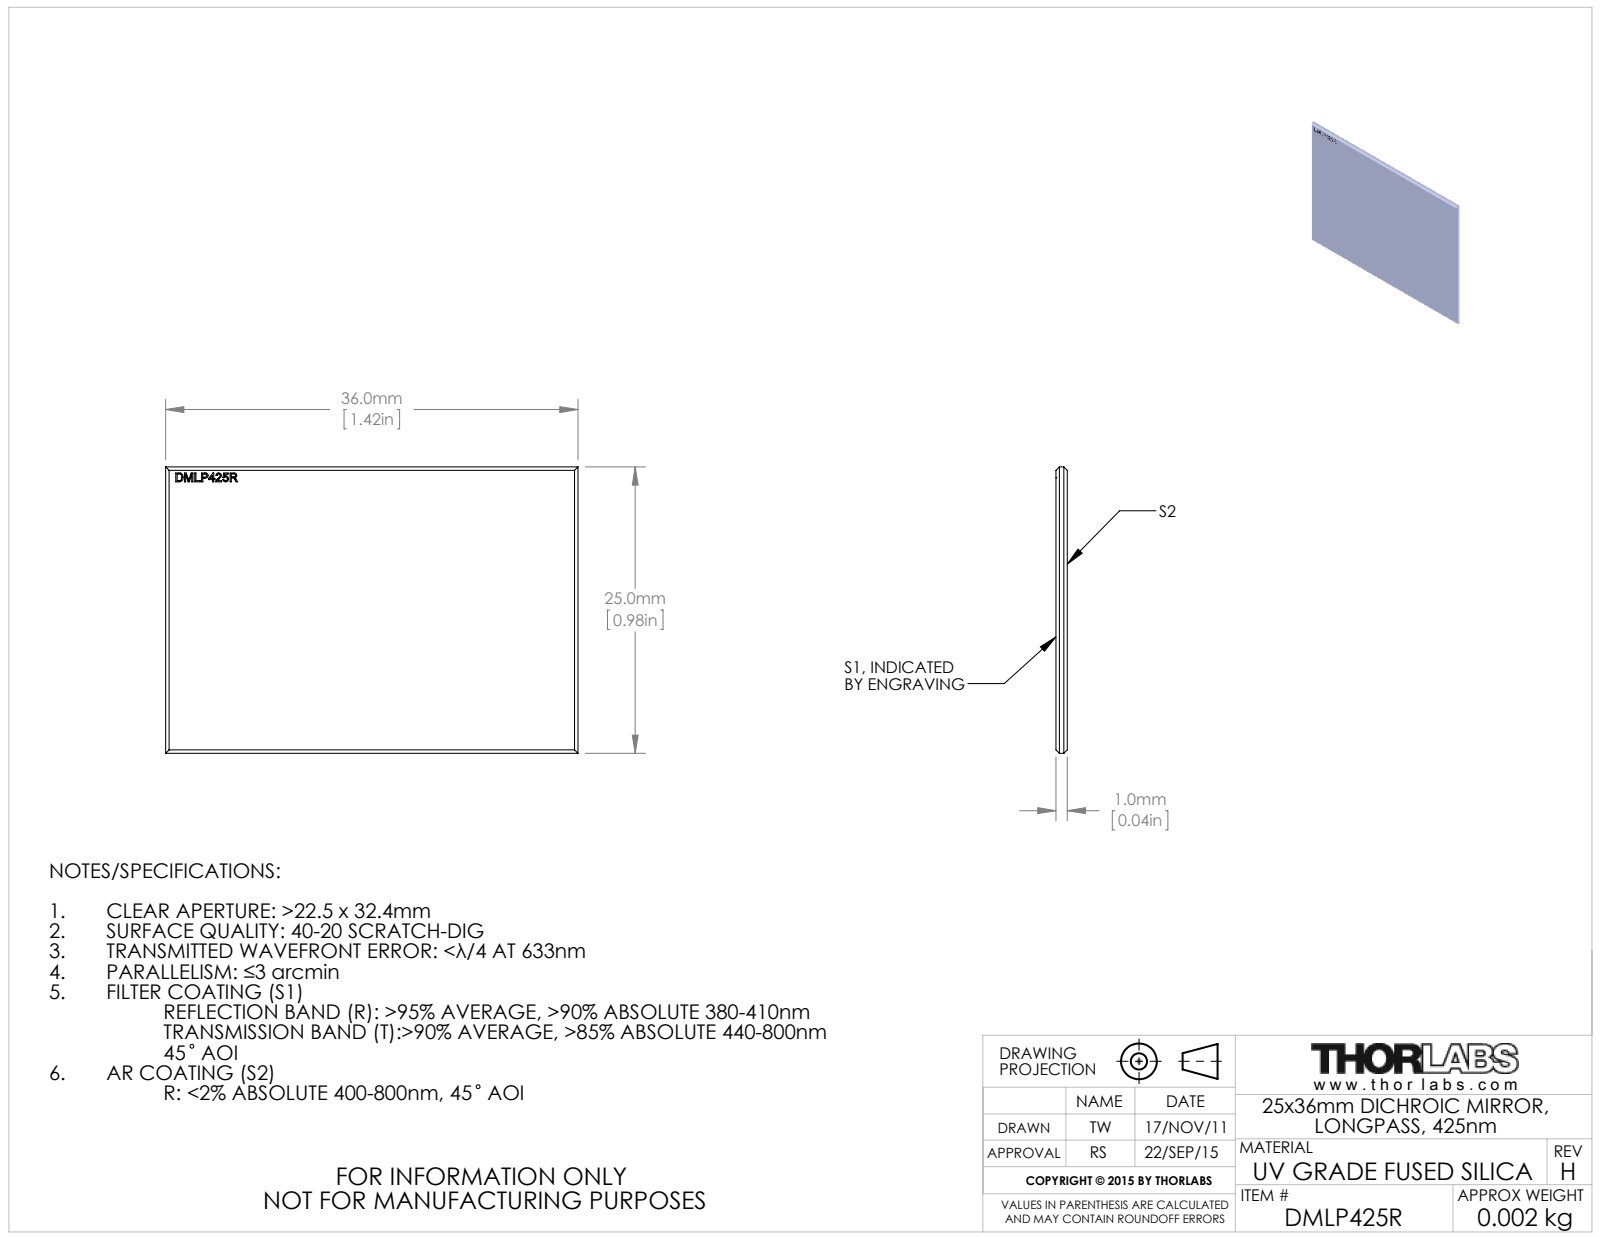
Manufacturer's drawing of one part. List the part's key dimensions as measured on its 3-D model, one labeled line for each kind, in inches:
Part name (STEP PRODUCT): 21095-E0W
STEP written by: SolidWorks 2011 (CONFIG_CONTROL_DESIGN)
Units: inches
Bodies: 0 solids, 52 faces (43 planar, 0 cylindrical, 9 other)
Overall size (bounding box): 1.417 × 0.984 × 0.039
Main face-to-face distances: 0.039, 0.707, 0.707, 0.984, 1.013, 1.013, 1.417, 0.039, 0.933, 0.051
